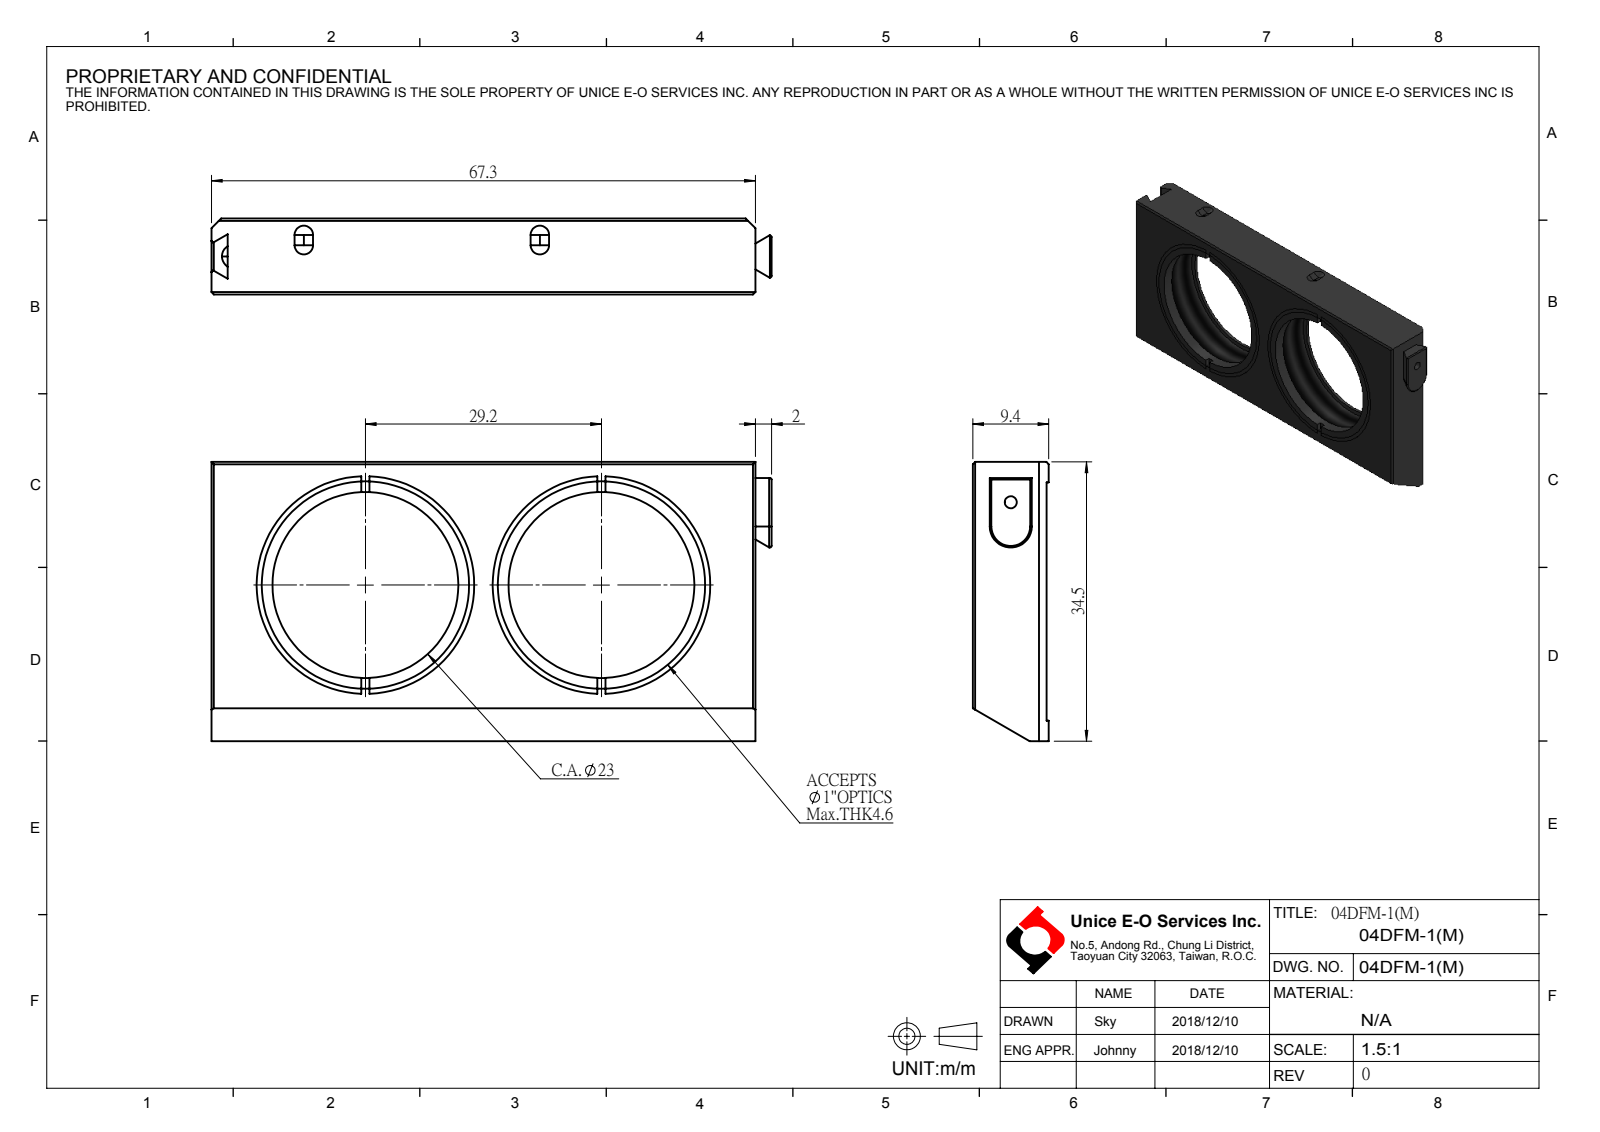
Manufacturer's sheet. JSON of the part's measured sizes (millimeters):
{"part_name": "04DFM-1(M)", "step_written_by": "SolidWorks 2016 (AUTOMOTIVE_DESIGN)", "units": "millimeters", "bodies": {"solids": 0, "faces": 94, "planar": 51, "cylindrical": 27, "other": 16}, "overall_size": [69.31, 34.54, 9.4], "round_holes": [[23, 2], [24, 2], [25.65, 2], [4.6, 1]], "partial_cylinders_radius": [[0.2, 5], [3, 1]], "face_to_face_distances": [9.15, 2, 9.4, 7.4, 7.15, 67.32, 34.54, 0.8, 8.6, 0.55], "hole_center_spacings": [29.21]}
